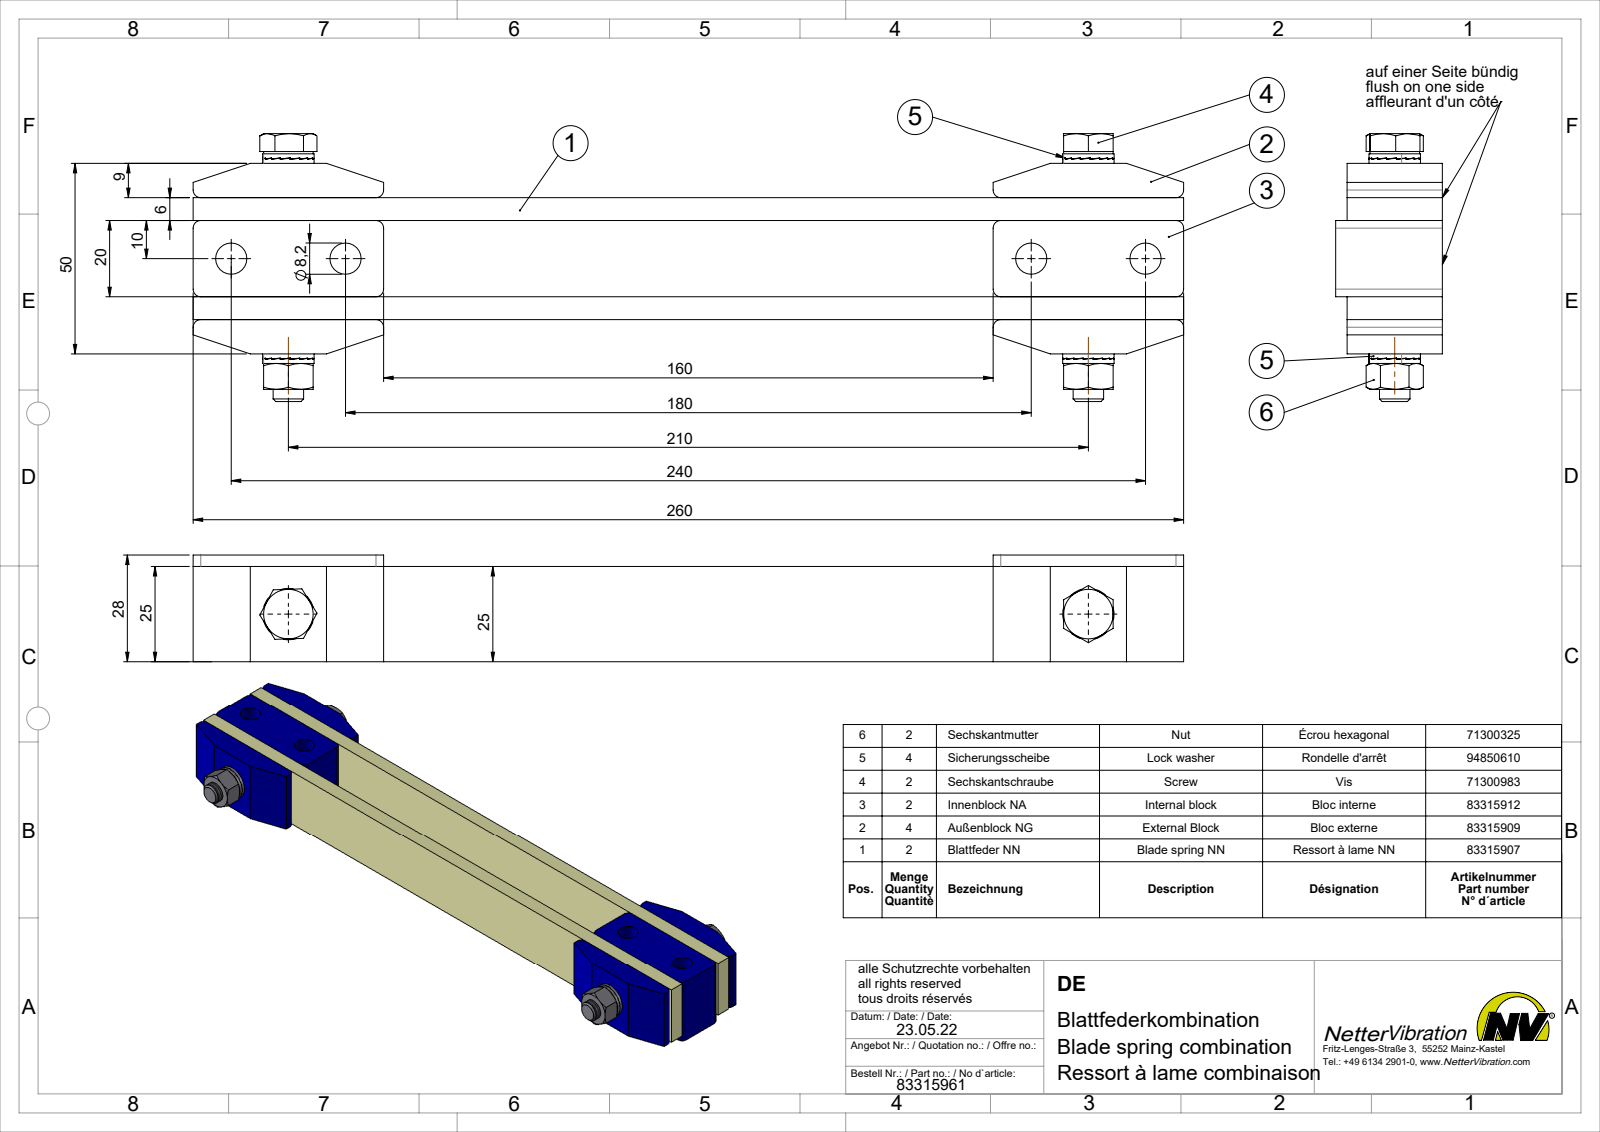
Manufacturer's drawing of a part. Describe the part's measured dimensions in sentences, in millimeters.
The part is named "Blattfederkombination DE # 83315961". Its 3-D file was written by "SolidWorks 2015 (AUTOMOTIVE_DESIGN)". It is 16 solids with 694 faces: 558 planar, 84 cylindrical and 52 other. Overall it measures 260 by 70.3 by 28 millimeters. Its volume is 170 207 cubic millimeters and its surface area 69 341 square millimeters. Round holes: 6 of diameter 8.2, 2 of diameter 6.8, 2 of diameter 8, 2 of diameter 8.5, 2 of diameter 8.7. Round bosses or shafts: 2 of diameter 13.5, 2 of diameter 13. Partial cylindrical surfaces (rounded edges, fillets, slot ends): 16 of radius 2. The main face-to-face distances are 6, 26, 20, 32, 25, 50, 9, 15, 35, 41. The hole center spacings are 210, 30, 180, 240.
